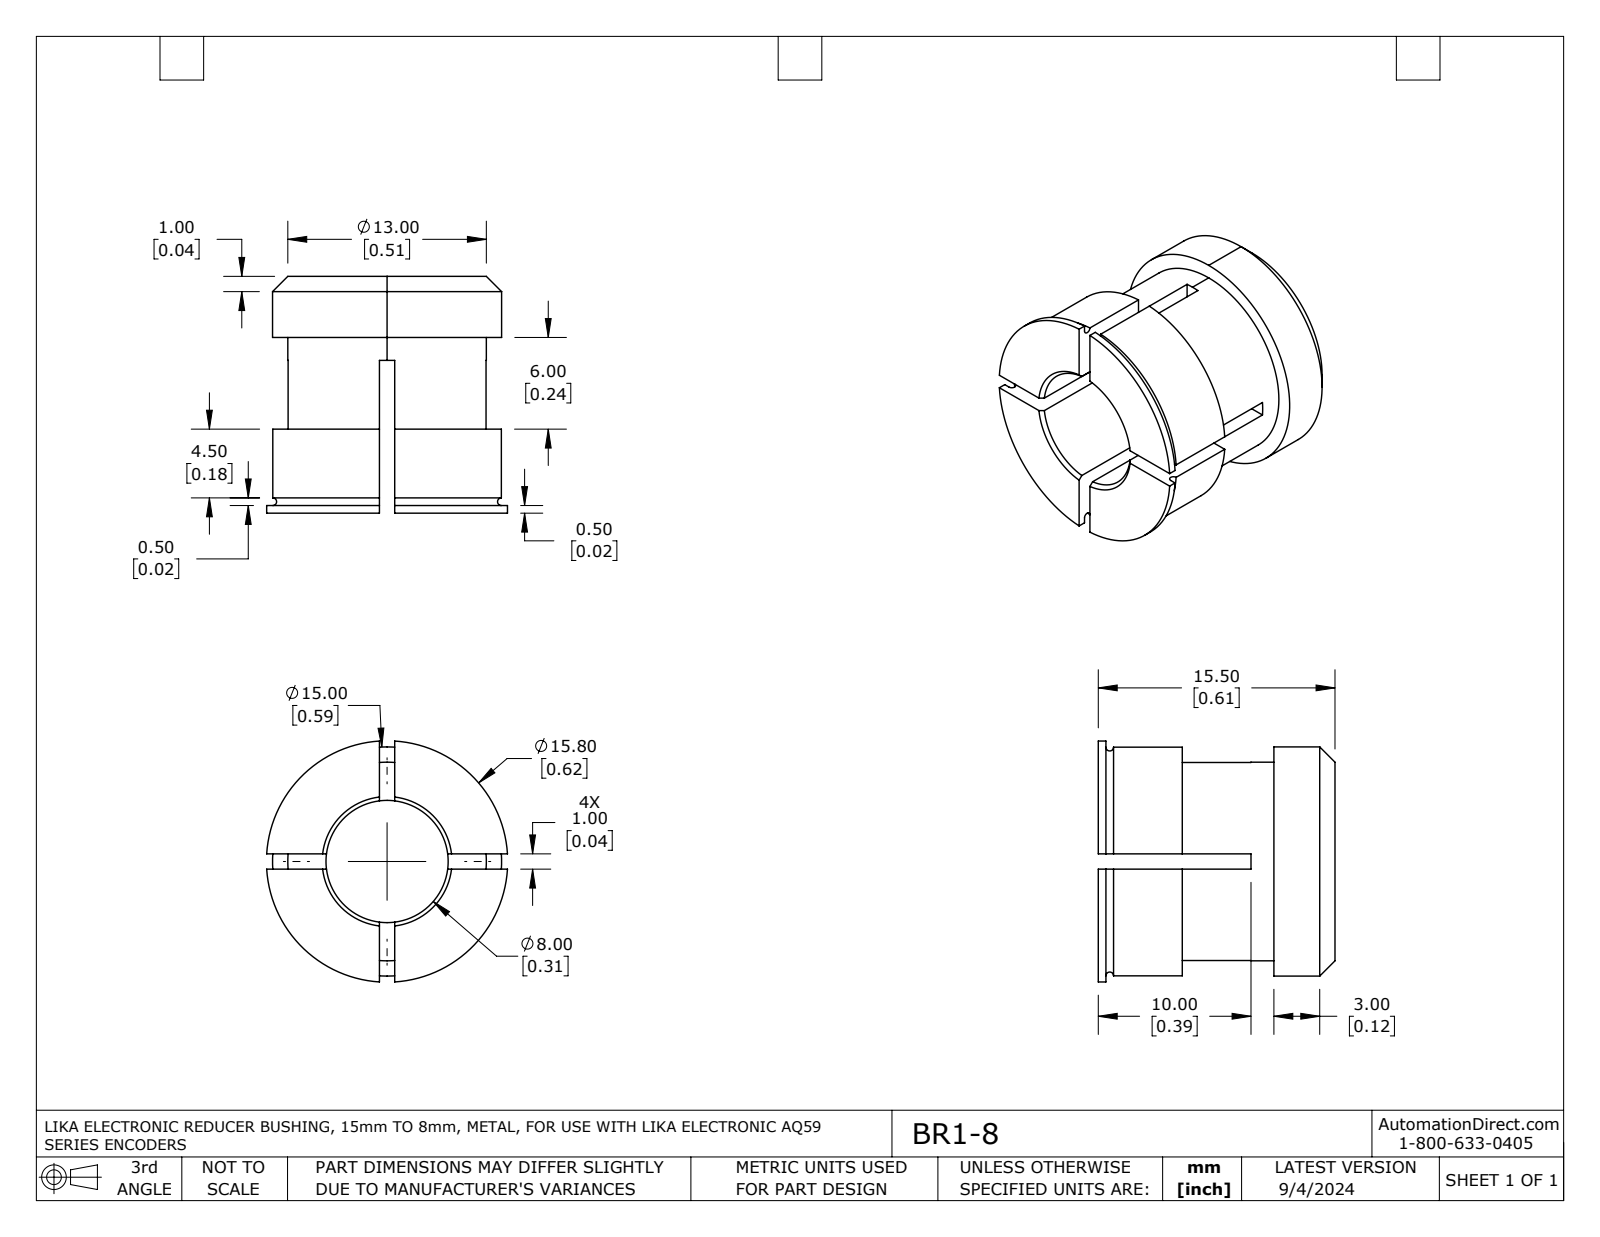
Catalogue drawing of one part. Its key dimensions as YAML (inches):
part_name: "BR1-8"
step_written_by: "SolidWorks 2021 (AUTOMOTIVE_DESIGN)"
units: inches
bodies: {solids: 1, faces: 54, planar: 26, cylindrical: 17, other: 11}
overall_size: [0.621, 0.621, 0.61]
volume: 0.095
surface_area: 2.475
round_holes:
  - {diameter: 0.315, count: 1}
round_bosses_or_shafts:
  - {diameter: 0.622, count: 1}
  - {diameter: 0.591, count: 1}
  - {diameter: 0.512, count: 1}
face_to_face_distances: [0.039, 0.61, 0.217, 0.394, 0.157, 0.453, 0.236, 0.591, 0.433, 0.197]
